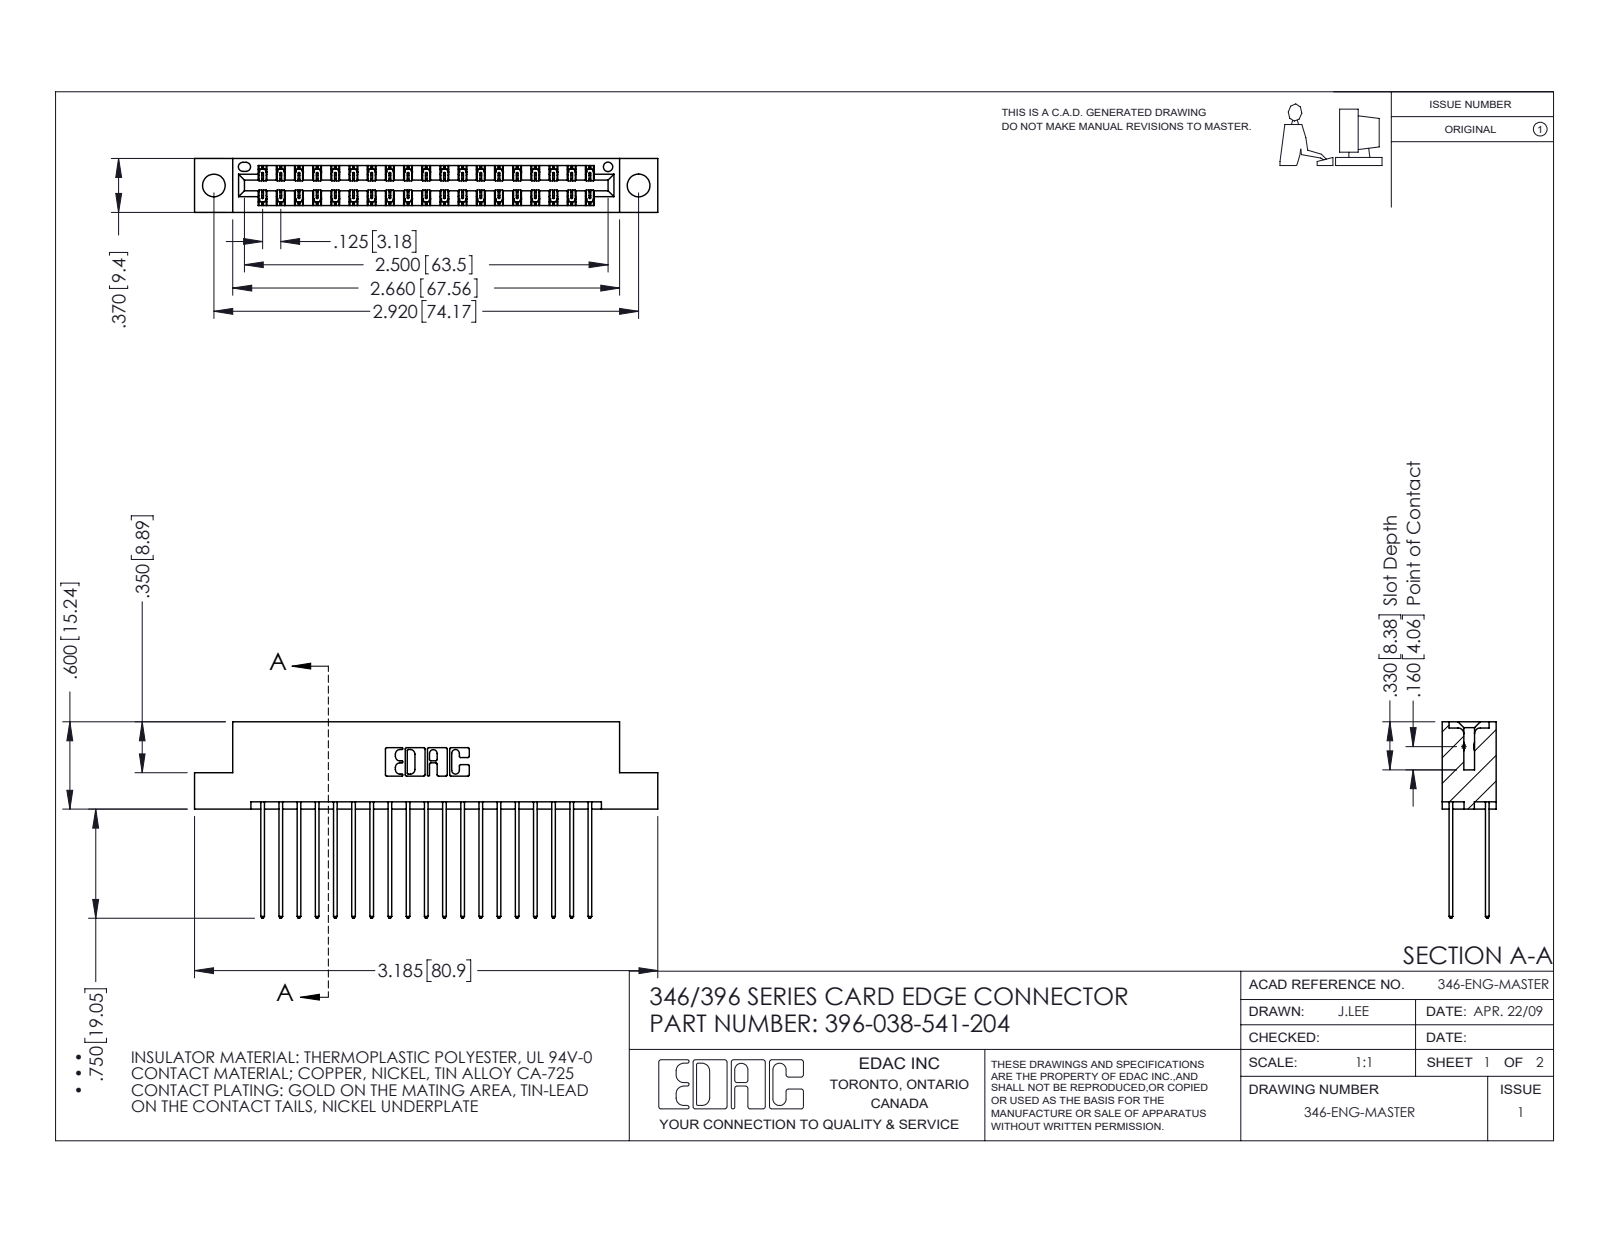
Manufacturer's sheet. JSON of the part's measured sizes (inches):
{"part_name": "396-038-541-204; 346 Part_Flush Mounting Lugs - 0.156 Dia-TH; 345-292-001_345-293-141", "step_written_by": "SolidWorks 2016 (CONFIG_CONTROL_DESIGN)", "units": "inches", "bodies": {"solids": 39, "faces": 2098, "planar": 1406, "cylindrical": 692, "other": 0}, "overall_size": [3.185, 1.35, 0.37], "volume_in3": 0.478, "surface_area_in2": 17.48, "round_holes": [[0.156, 2], [0.064, 1]], "partial_cylinders_radius": [[0.006, 57], [0.01, 38], [0.01, 22], [0.007, 6], [0.031, 6], [0.026, 3], [0.014, 2], [0.022, 2]], "face_to_face_distances": [0.048, 0.322, 0.25, 0.072, 0.298, 0.025, 0.37, 0.275, 0.148, 0.222], "hole_center_spacings": [0.246, 2.713, 2.92]}
